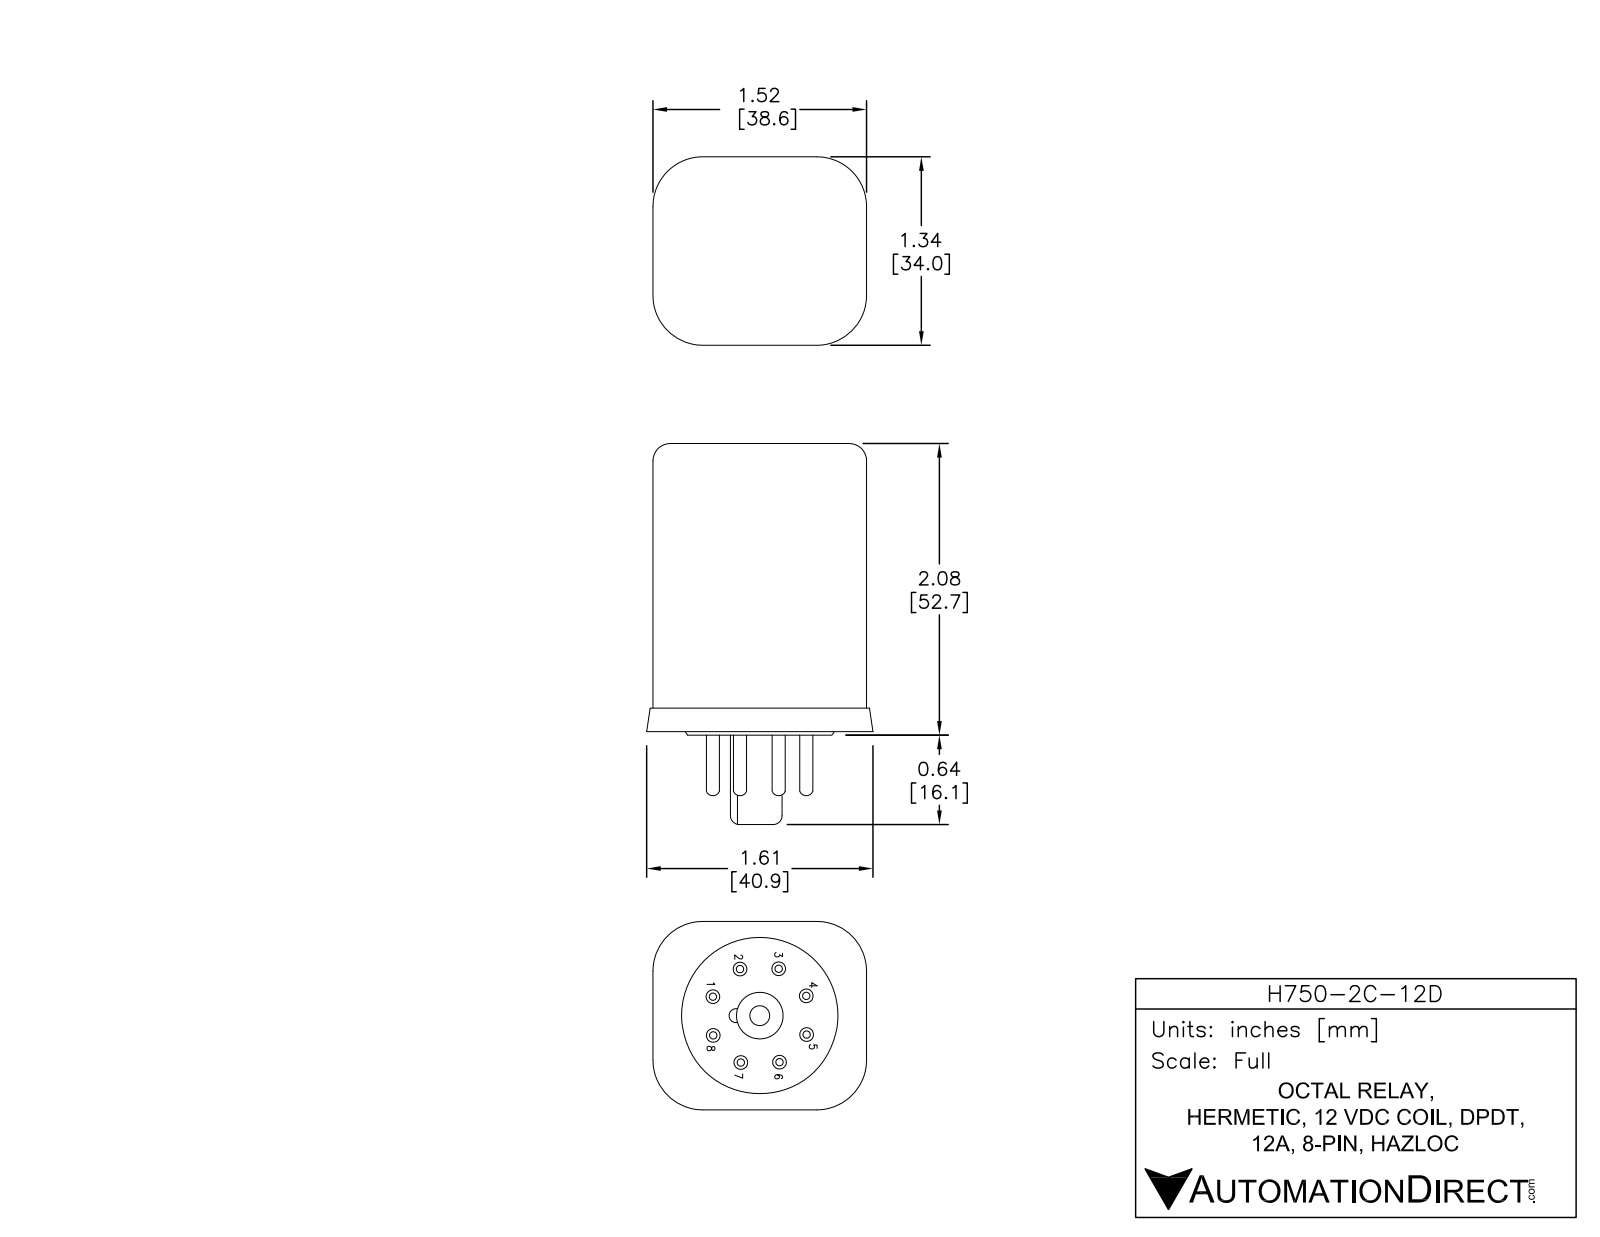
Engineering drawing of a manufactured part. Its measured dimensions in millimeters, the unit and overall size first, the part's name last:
Units: millimetres
Overall size (bounding box): 67.3 × 41.35 × 36.6
Round holes (diameter × count): ⌀4.5 ×8, ⌀3.9 ×1
Round bosses / shafts (diameter × count): ⌀2.31 ×8, ⌀27 ×1, ⌀12 ×1, ⌀8 ×1
Partial cylindrical surfaces — rounded edges, fillets, slot ends (radius × count): R0.62 ×8, R2.5 ×4, R10 ×4, R11.3 ×4, R0.5 ×2, R0.59 ×1
Main face-to-face distances: 53, 34, 38.75, 0.5, 53.5, 1.3, 35.3, 40.05, 1, 54
Hole centre spacings: 8.5, 12.02, 15.7, 6.5, 6.51, 16.99
Volume: 66 961 mm³ · Surface area: 10 714 mm²
Bodies: 1 solid, 268 faces (108 planar, 65 cylindrical, 95 other)
Part name (STEP PRODUCT): H750-2C-12D
STEP written by: SolidWorks 2013 (AUTOMOTIVE_DESIGN)
